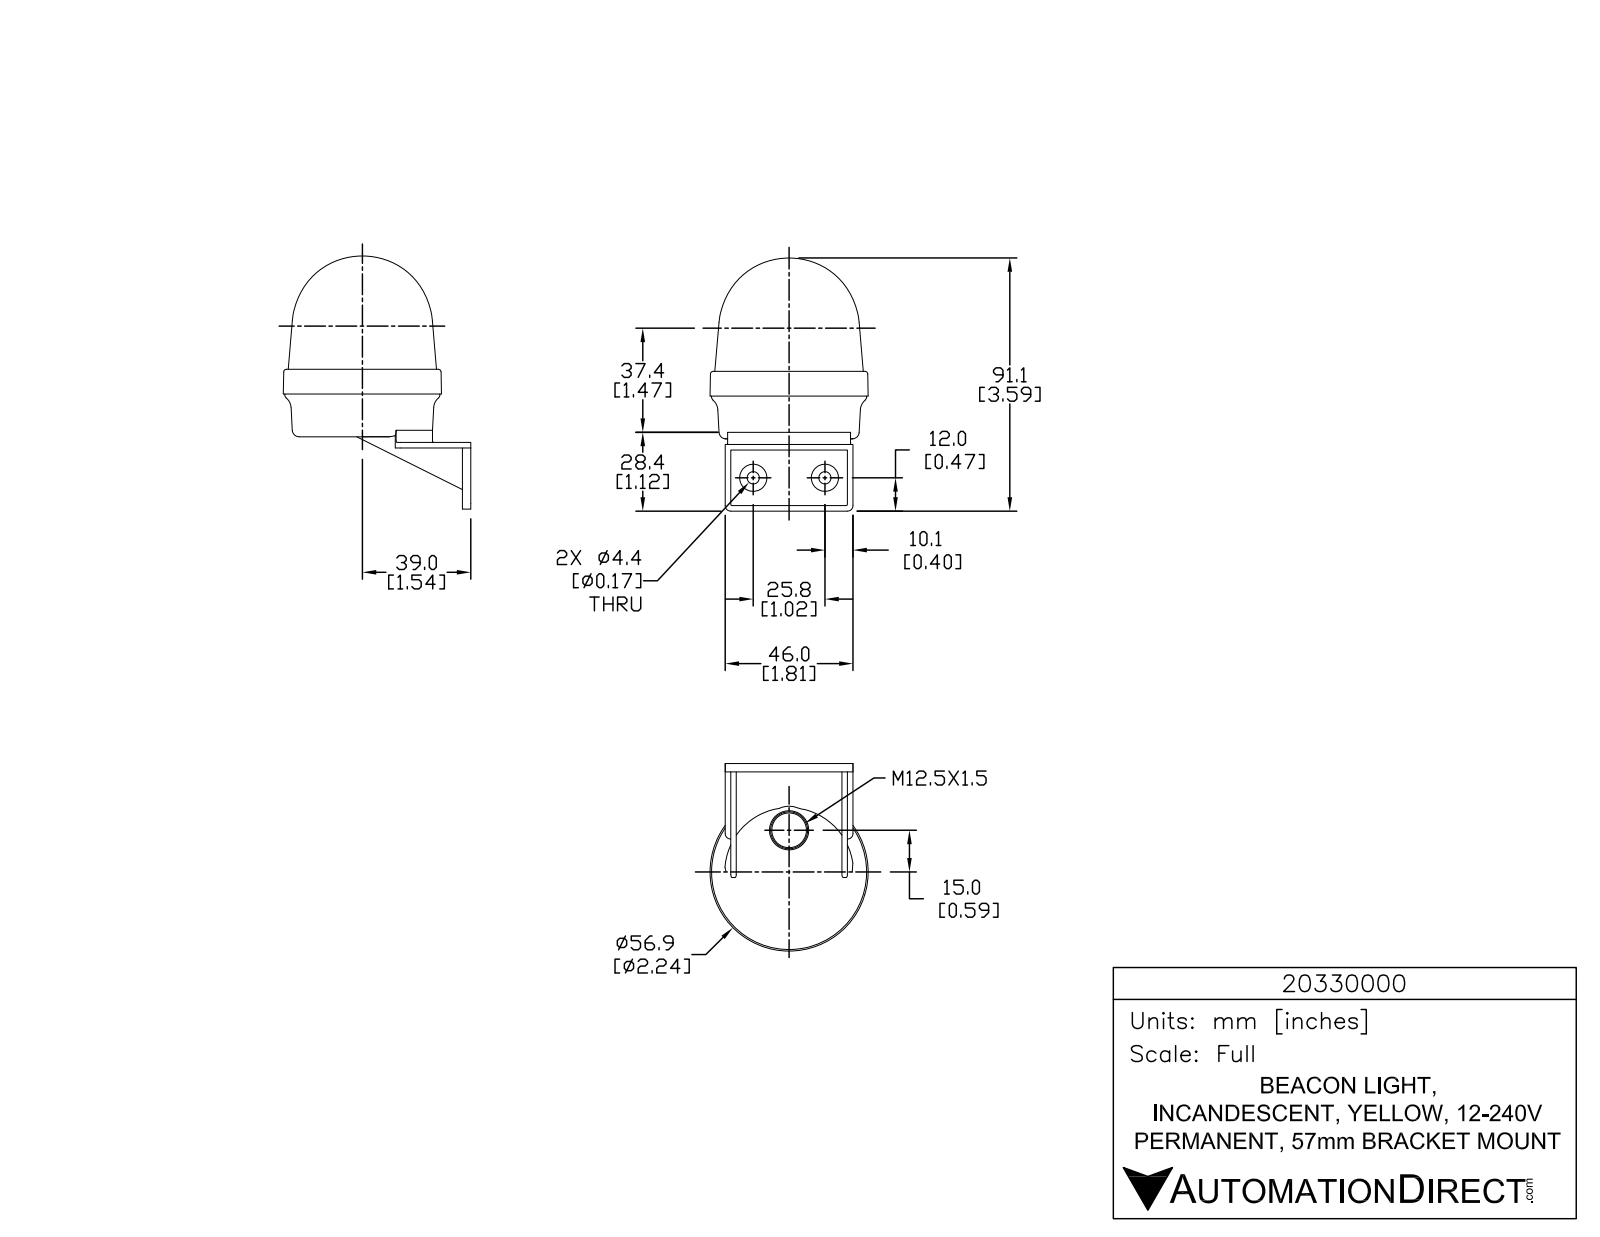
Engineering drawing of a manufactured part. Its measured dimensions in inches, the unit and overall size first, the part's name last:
Units: inches
Overall size (bounding box): 3.587 × 2.837 × 2.392
Round holes (diameter × count): ⌀0.039 ×3, ⌀0.173 ×2
Round bosses / shafts (diameter × count): ⌀0.226 ×3, ⌀0.056 ×3, ⌀0.386 ×2, ⌀2.197 ×1
Partial cylindrical surfaces — rounded edges, fillets, slot ends (radius × count): R0.008 ×6, R0.008 ×6, R0.008 ×6, R0.02 ×6, R0.131 ×6, R0.079 ×4, R0.004 ×3, R0.005 ×3
Main face-to-face distances: 0.079, 0.157, 1.575, 1.654, 0.039, 0.118, 1.496, 0.866, 0.945, 1.733
Hole centre spacings: 1.016
Volume: 7.74 in³ · Surface area: 28.71 in²
Bodies: 1 solid, 813 faces (550 planar, 169 cylindrical, 94 other)
Part name (STEP PRODUCT): 20330000
STEP written by: SolidWorks 2015 (AUTOMOTIVE_DESIGN)
